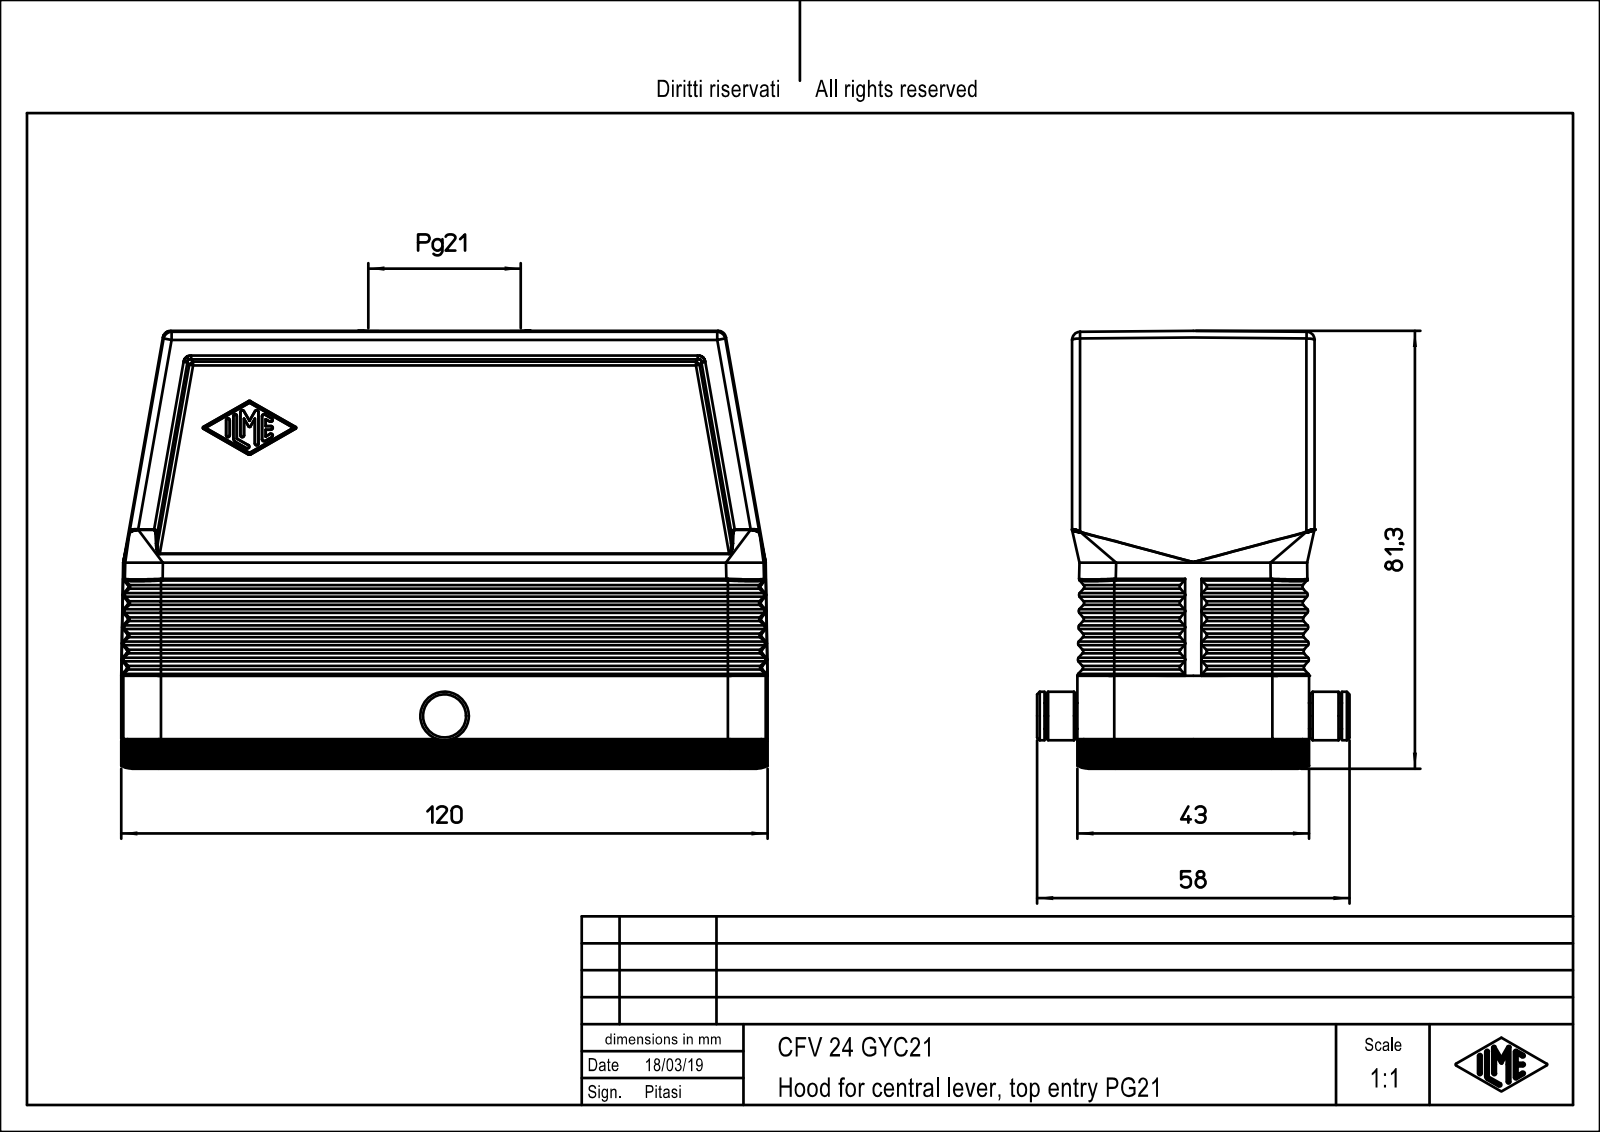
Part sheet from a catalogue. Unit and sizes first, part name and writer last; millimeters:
Units: millimetres
Overall size (bounding box): 120 × 81.25 × 58
Round holes (diameter × count): ⌀3 ×4, ⌀27.54 ×1
Round bosses / shafts (diameter × count): ⌀9 ×1, ⌀4.8 ×1
Partial cylindrical surfaces — rounded edges, fillets, slot ends (radius × count): R0.5 ×84, R1 ×16, R7 ×12, R1.5 ×10, R3 ×8, R3.5 ×4, R4 ×4, R4.2 ×4
Main face-to-face distances: 43, 1.01, 4, 2, 6, 39, 1, 5, 40, 44
Hole centre spacings: 27, 53.71, 53.72, 103.99, 107.44
Volume: 125 504 mm³ · Surface area: 58 765 mm²
Bodies: 1 solid, 573 faces (223 planar, 182 cylindrical, 168 other)
Part name (STEP PRODUCT): CFV_24_GYC21
STEP written by: PTC Creo Elements/Direct Modeling 19.0E 27-Jun-2016 (C) Parametric Technology GmbH (AUTOMOTIVE_DESIGN)
